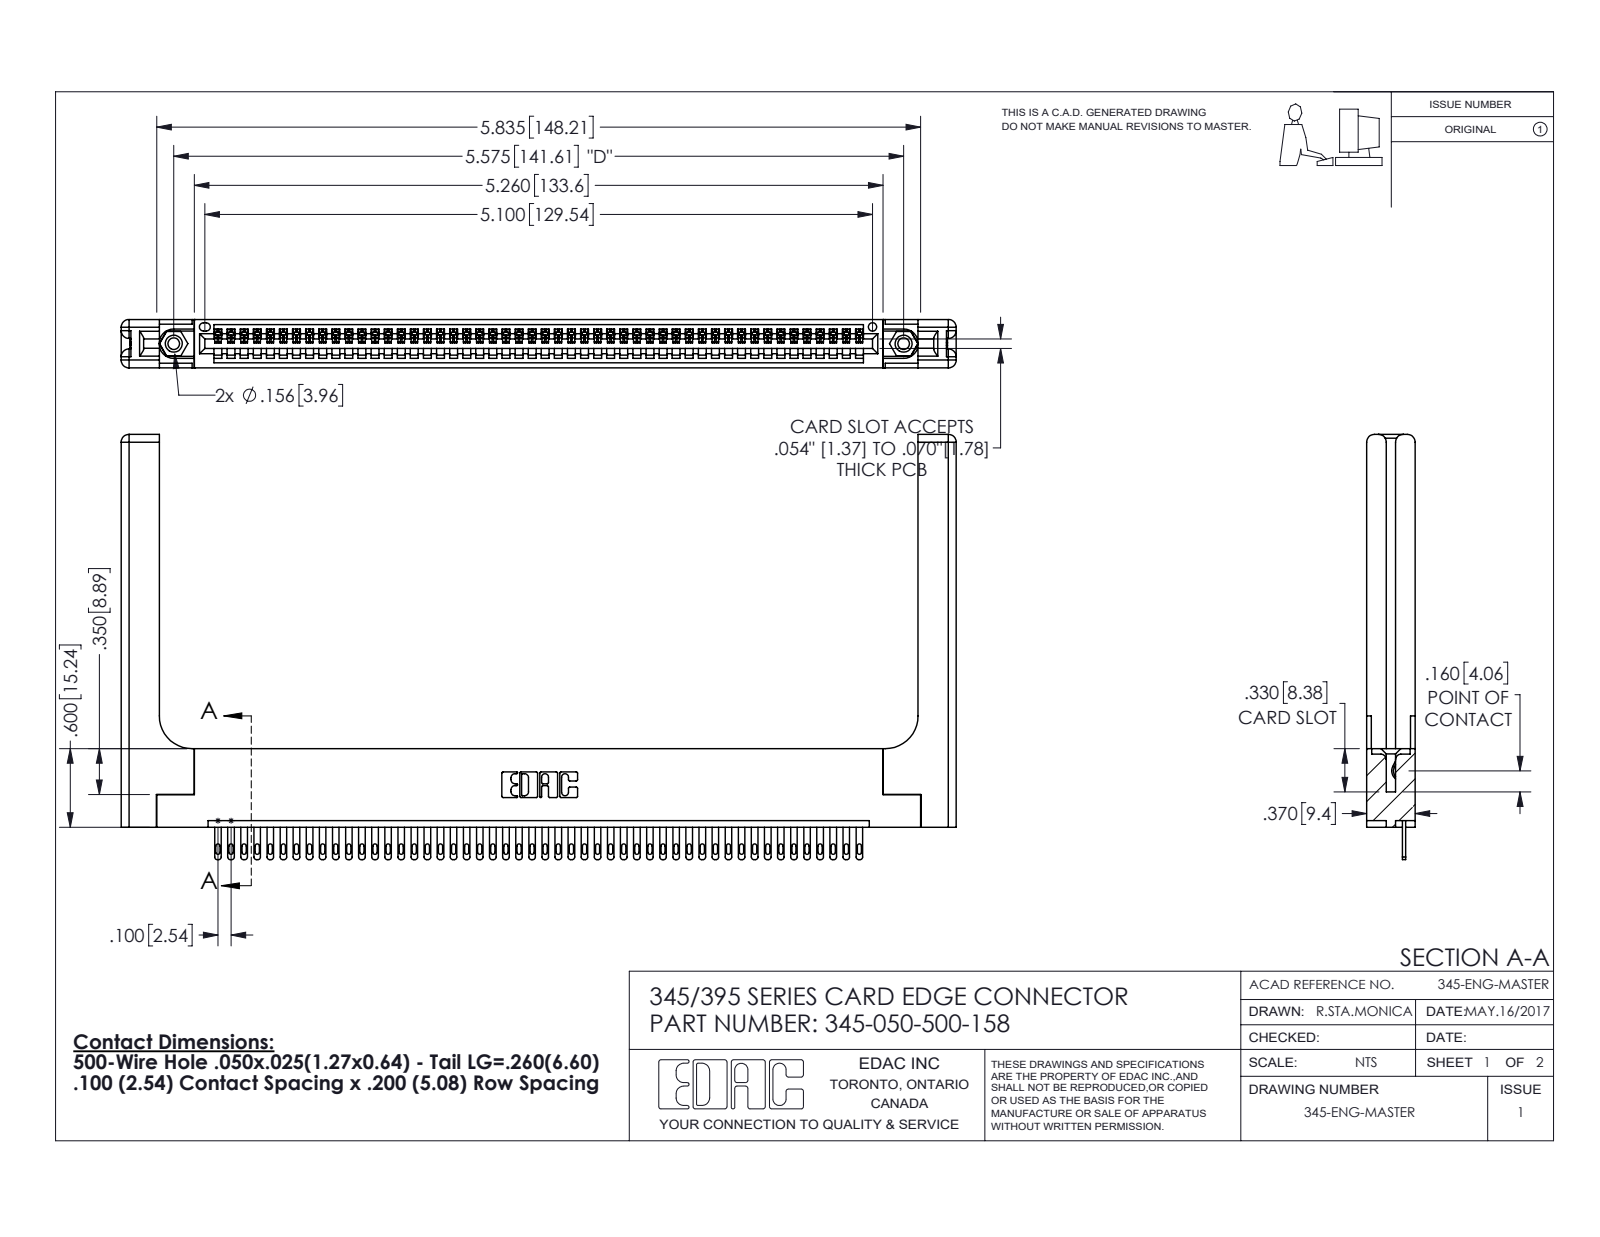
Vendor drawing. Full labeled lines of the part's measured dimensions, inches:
Part name (STEP PRODUCT): 345 Part_Flush Mounting Lugs - 0.156 Dia-TH; 345-250-001_345-250-001-102; 345-220-058_345-220-058; 345-292-001_345-293-100 (+1 more)
STEP written by: SolidWorks 2016 (CONFIG_CONTROL_DESIGN)
Units: inches
Bodies: 55 solids, 3082 faces (1928 planar, 1094 cylindrical, 60 other)
Overall size (bounding box): 6.379 × 3.247 × 0.37
Volume: 1.464 in³ · Surface area: 40.46 in²
Round holes (diameter × count): ⌀0.089 ×2, ⌀0.125 ×2, ⌀0.156 ×2, ⌀0.064 ×1
Round bosses / shafts (diameter × count): ⌀0.155 ×2
Partial cylindrical surfaces — rounded edges, fillets, slot ends (radius × count): R0.006 ×100, R0.016 ×100, R0.02 ×100, R0.01 ×22, R0.06 ×16, R0.007 ×6, R0.031 ×6, R0.026 ×3
Main face-to-face distances: 0.072, 0.37, 0.298, 0.2, 0.098, 0.272, 0.025, 0.225, 0.148, 0.15
Hole centre spacings: 0.27, 5.339, 5.575
